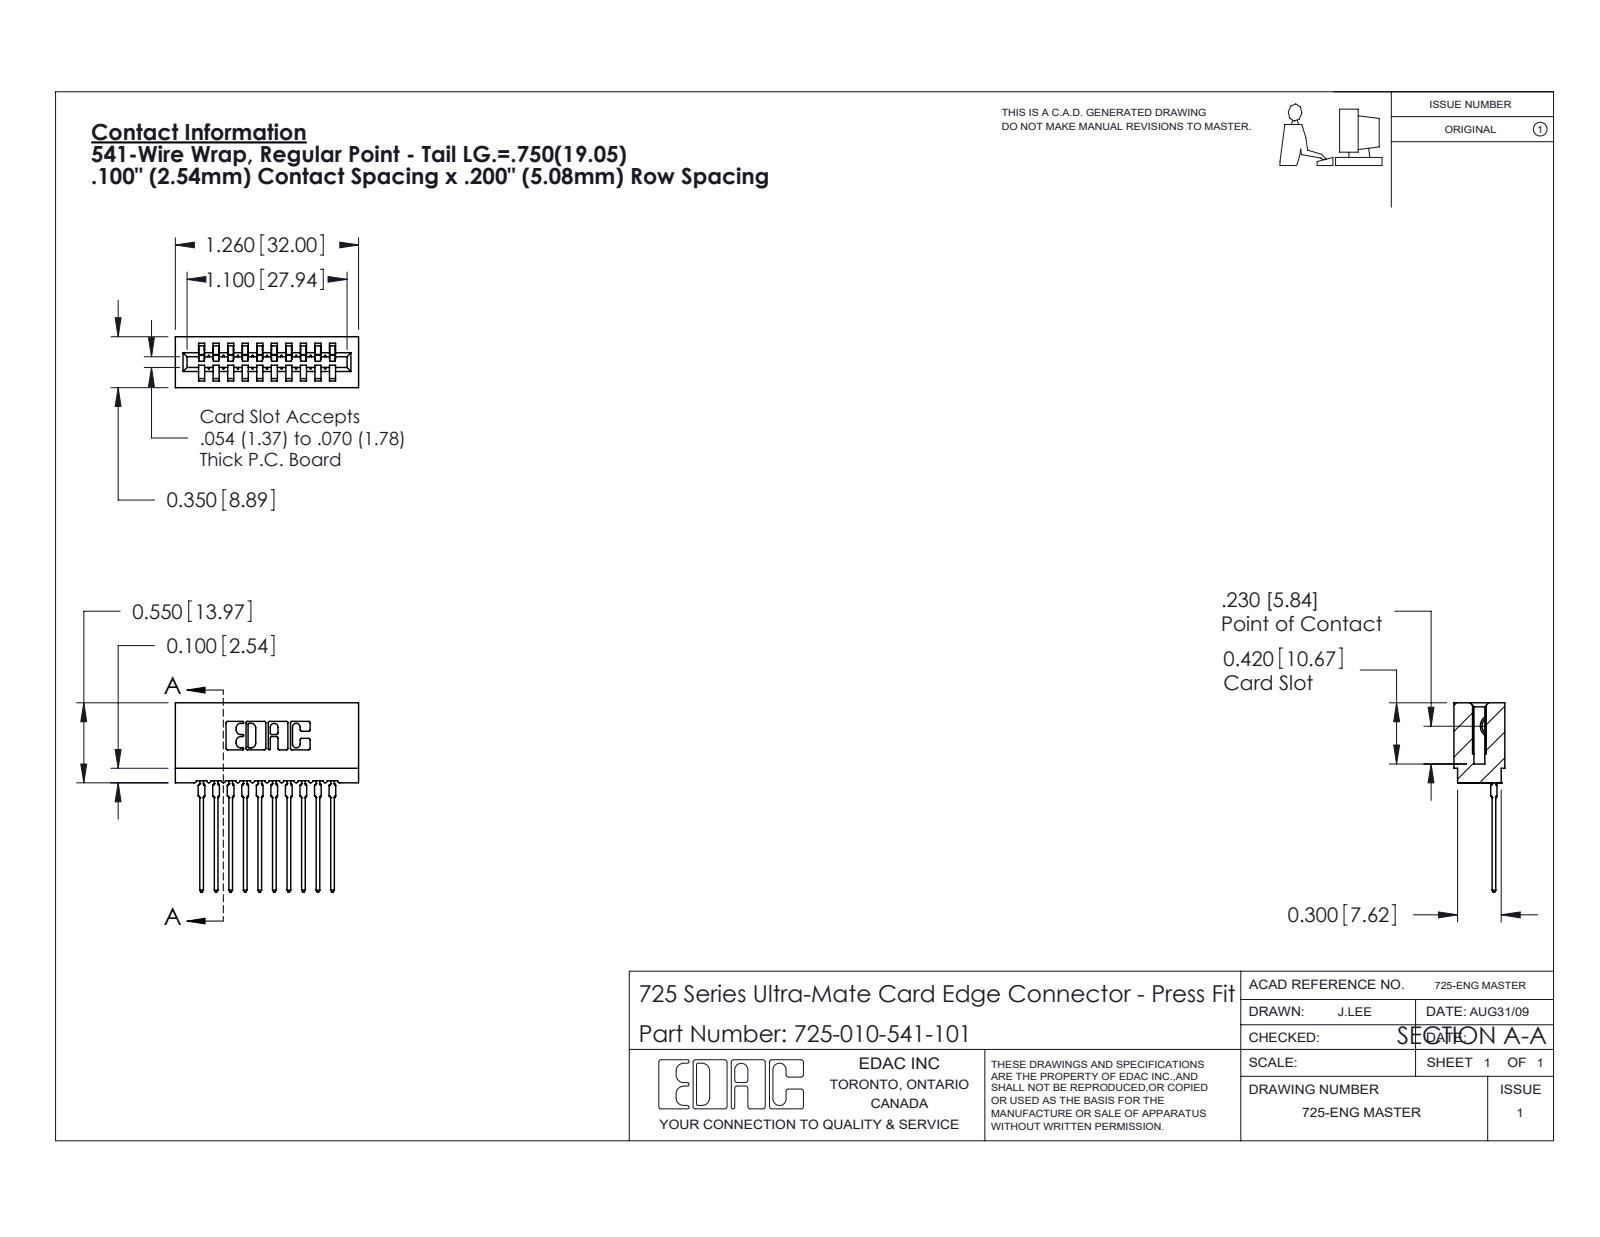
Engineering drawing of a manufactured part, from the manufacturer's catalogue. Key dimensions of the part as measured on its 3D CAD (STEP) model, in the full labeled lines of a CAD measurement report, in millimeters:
Part name (STEP PRODUCT): 725-010-541-101; 745-292-001_541; 725 Part_Insulator Option - 01
STEP written by: SolidWorks 2020 (CONFIG_CONTROL_DESIGN)
Units: millimetres
Bodies: 11 solids, 1215 faces (725 planar, 230 cylindrical, 260 other)
Overall size (bounding box): 33 × 32 × 8.9
Volume: 2 650 mm³ · Surface area: 4 715 mm²
Partial cylindrical surfaces — rounded edges, fillets, slot ends (radius × count): R0.3 ×22, R0.4 ×20, R0.5 ×20, R0.2 ×6, R0.8 ×6, R0.1 ×4, R0.3 ×4, R0.7 ×3
Main face-to-face distances: 2.5, 5.1, 7.6, 10.2, 1.1, 12.7, 3.6, 1.5, 6.1, 4
